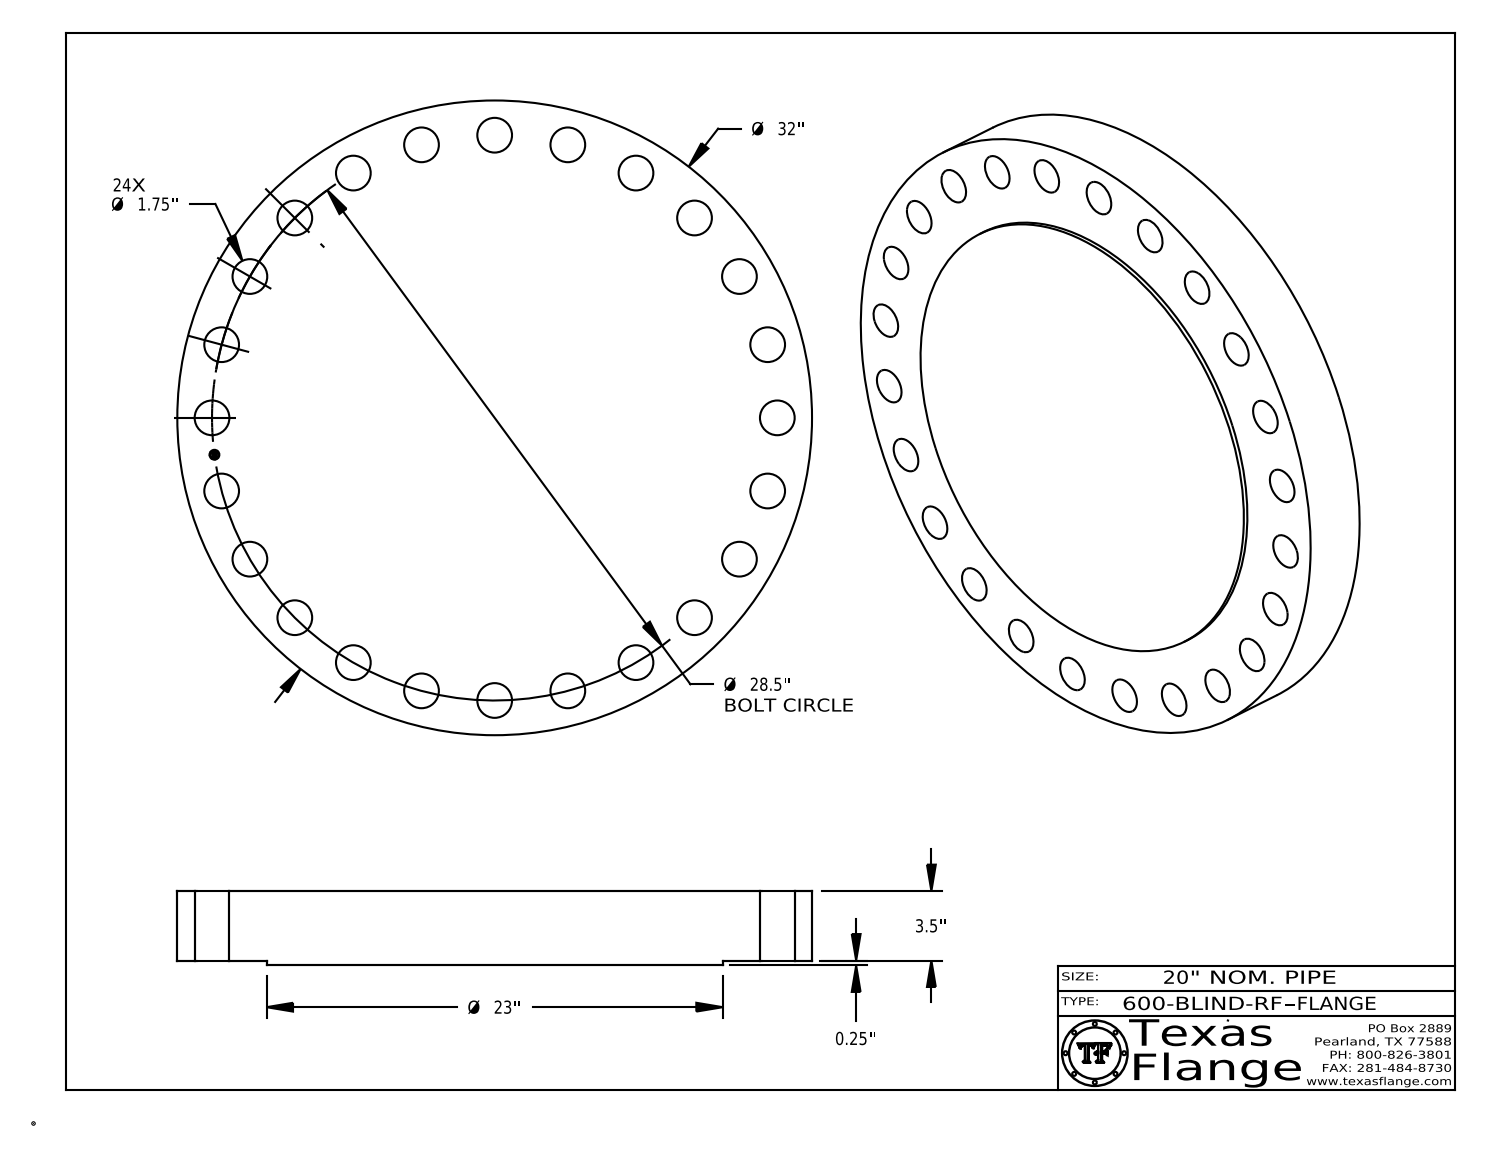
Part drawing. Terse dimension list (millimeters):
name: 600-BLIND-RF
written by: CATIA V5 STEP AP214 (AUTOMOTIVE_DESIGN)
unit: mm
bodies: 1 solid, 440 faces (368 planar, 72 cylindrical, 0 other)
size: 812.8 × 812.8 × 95.3
volume: 44 520 000 mm³; area: 1 500 000 mm²
holes: 24× ⌀44.5, 1× ⌀12.6
bosses: 8× ⌀0.8, 1× ⌀812.8, 1× ⌀584.2, 1× ⌀9.9
face distances: 95.3, 6.4, 88.9, 0.4, 94.9, 88.5, 3.8, 3.7, 0.7, 2.4
hole spacings: 94.5, 187.4, 626.9, 668.8, 699.2, 362, 511.9, 277
